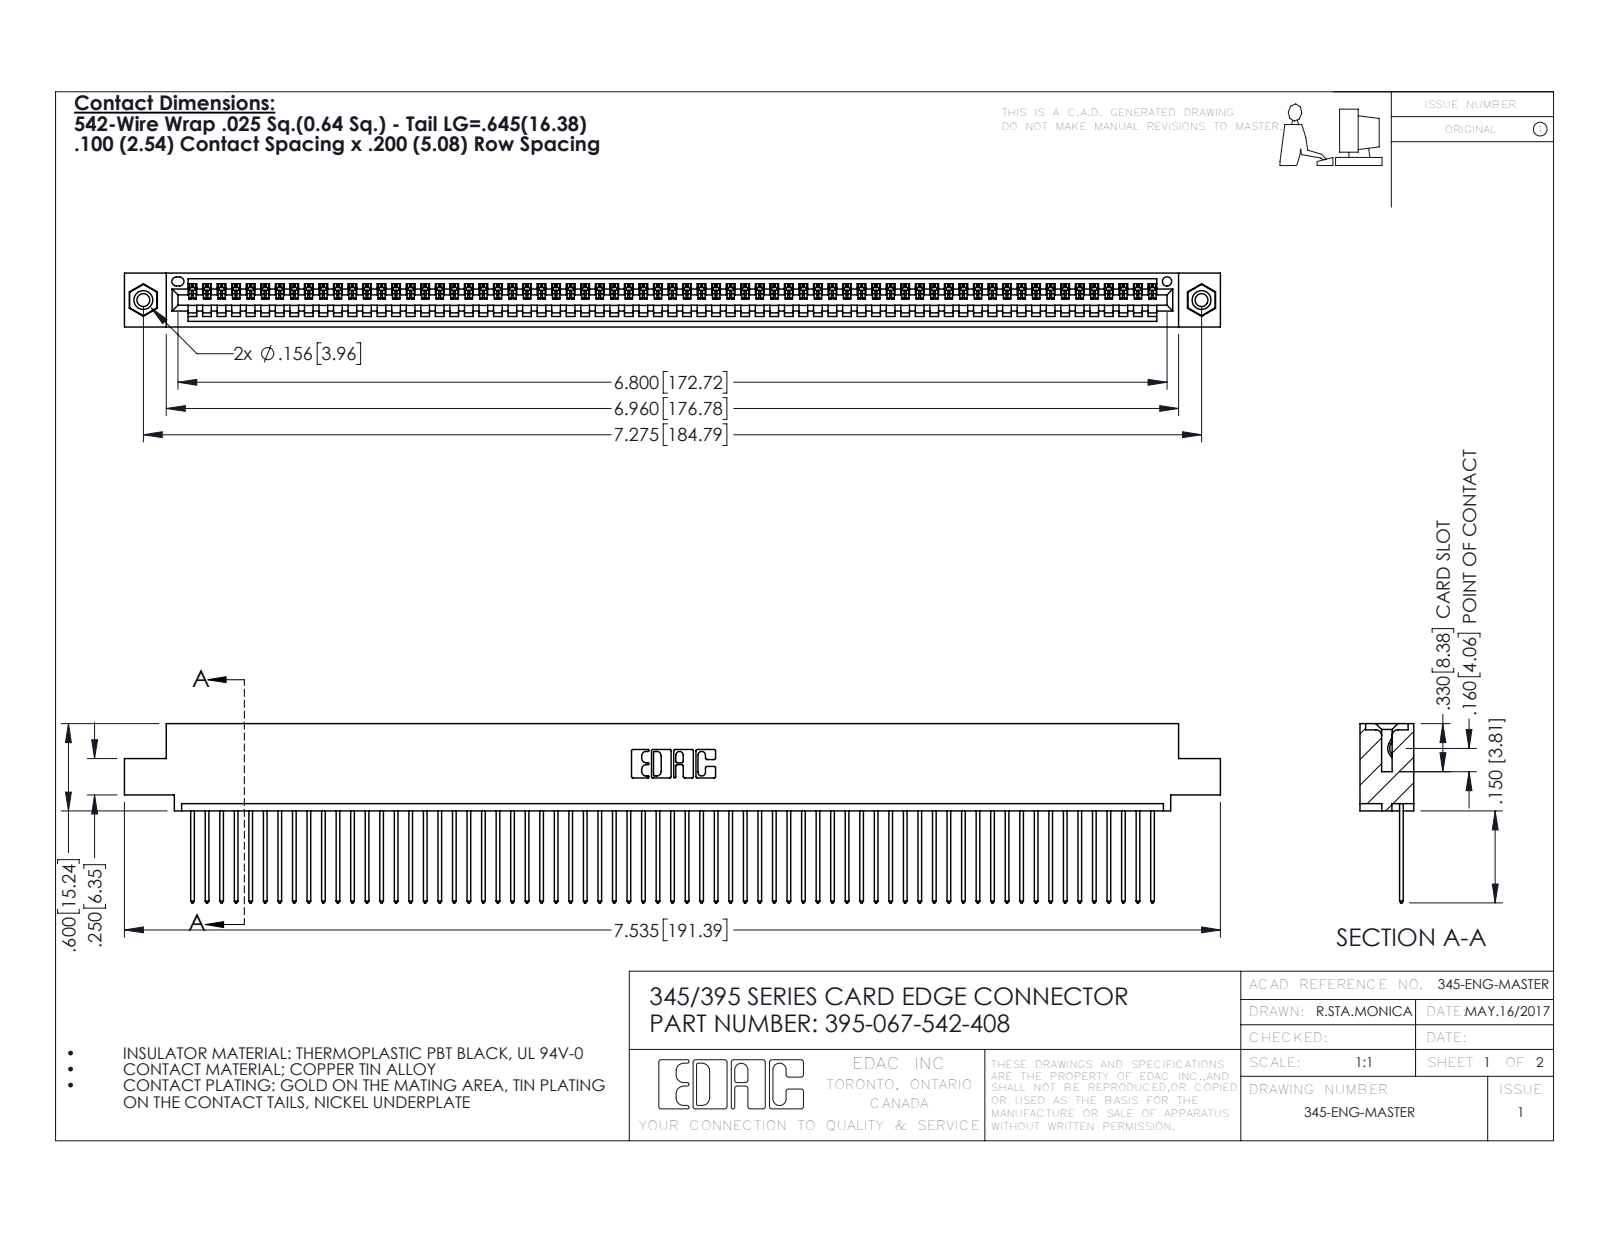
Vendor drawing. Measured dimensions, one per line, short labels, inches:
name: 345-250-001_345-250-003-102; 395-067-542-408; 345 Part_0.110 Offset - 0.156 Dia-TI; 345-292-001_345-293-142
written by: SolidWorks 2016 (CONFIG_CONTROL_DESIGN)
unit: in
bodies: 70 solids, 4076 faces (2796 planar, 1264 cylindrical, 16 other)
size: 7.535 × 1.232 × 0.37
volume: 1.126 in³; area: 40.15 in²
holes: 2× ⌀0.089, 2× ⌀0.125, 2× ⌀0.156, 1× ⌀0.064
bosses: 2× ⌀0.155
rounds: 134× R0.006, 134× R0.01, 22× R0.01, 6× R0.007, 6× R0.031, 3× R0.026, 2× R0.031, 2× R0.04
face distances: 0.072, 0.298, 0.098, 0.272, 0.025, 0.37, 0.2, 0.225, 0.149, 0.072
hole spacings: 0.27, 7.039, 7.275
